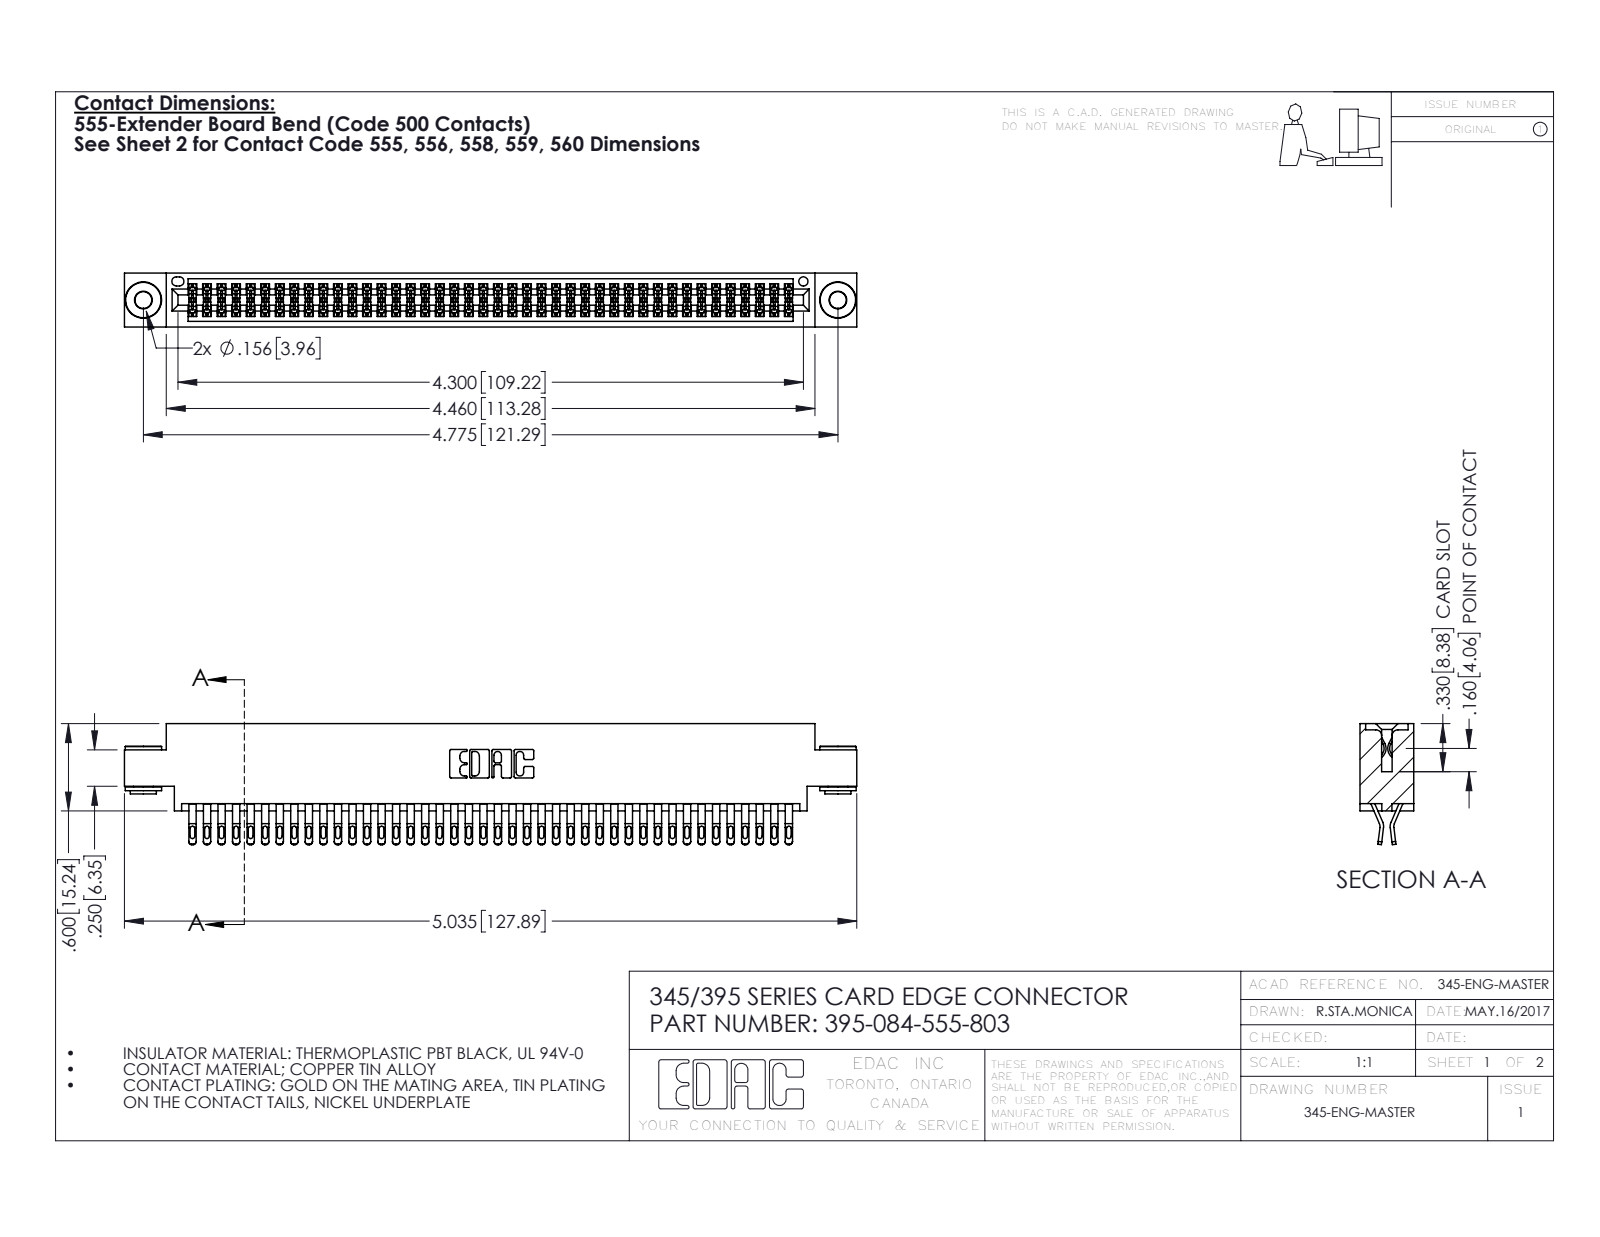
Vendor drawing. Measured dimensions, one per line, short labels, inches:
name: 395-084-555-803; 345-292-001_555 Tail; 345-250-002_345-250-002-102; 345 Part_0.170 Offset - 0.156 Dia-TH
written by: SolidWorks 2016 (CONFIG_CONTROL_DESIGN)
unit: in
bodies: 87 solids, 4872 faces (2698 planar, 2166 cylindrical, 8 other)
size: 5.035 × 0.832 × 0.37
volume: 0.767 in³; area: 30.66 in²
holes: 2× ⌀0.116, 2× ⌀0.156, 1× ⌀0.064
bosses: 2× ⌀0.25, 2× ⌀0.18, 2× ⌀0.136
rounds: 210× R0.016, 168× R0.02, 126× R0.006, 22× R0.01, 6× R0.007, 6× R0.031, 3× R0.026, 2× R0.01
face distances: 0.072, 0.298, 0.37, 0.025, 0.2, 0.098, 0.272, 0.225, 0.175, 0.149
hole spacings: 0.27, 4.539, 4.775
